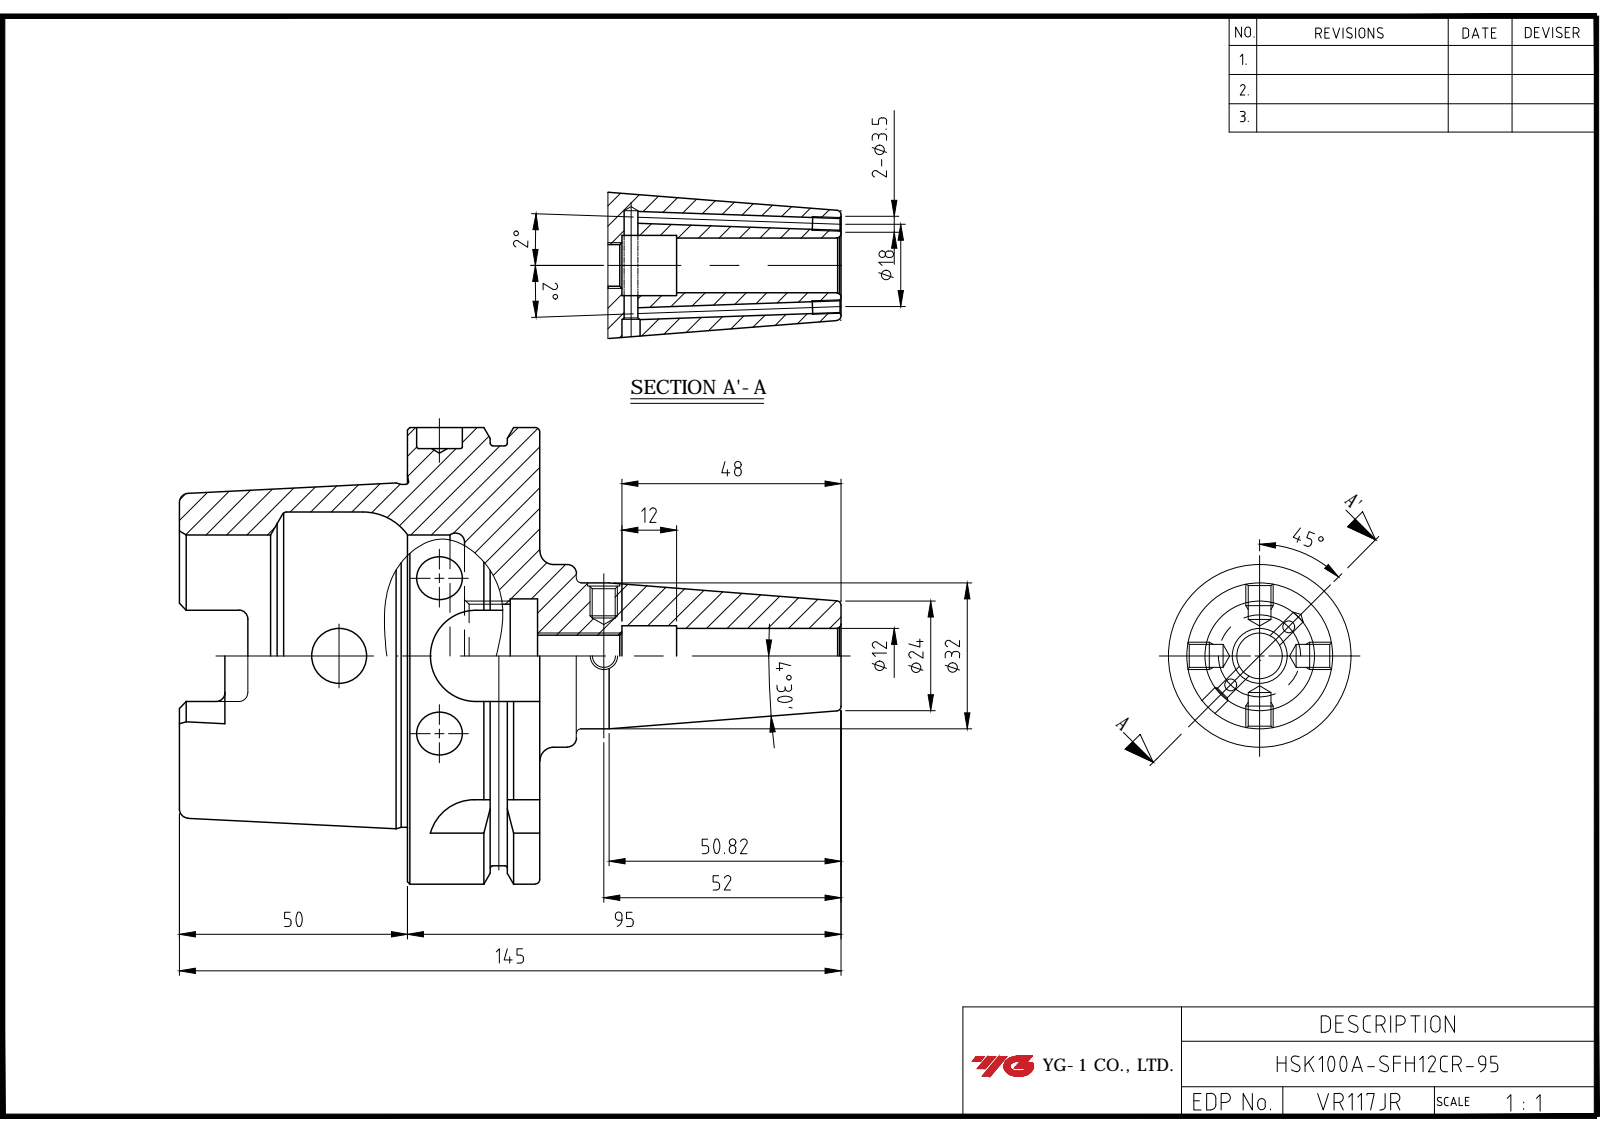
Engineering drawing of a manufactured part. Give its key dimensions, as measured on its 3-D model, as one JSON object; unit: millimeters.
{"part_name": "LO-HSK100A-SFH12CR-95", "step_written_by": "Autodesk Inventor 2024 (AUTOMOTIVE_DESIGN)", "units": "millimeters", "bodies": {"solids": 1, "faces": 124, "planar": 39, "cylindrical": 38, "other": 47}, "overall_size": [145, 100, 100], "volume_mm3": 294137, "surface_area_mm2": 58278, "round_holes": [[2.46, 2], [12, 2], [8.92, 1], [10, 1], [13.2, 1], [22.38, 1], [25, 1], [53, 1], [63, 1]], "round_bosses_or_shafts": [[100, 1], [92, 1], [75.41, 1], [40, 1], [32, 1]], "partial_cylinders_radius": [[2, 6], [4.88, 4], [10, 4]], "face_to_face_distances": [29, 12.5, 16.5, 62.5, 50, 79, 88, 78.5, 28.5, 16]}
